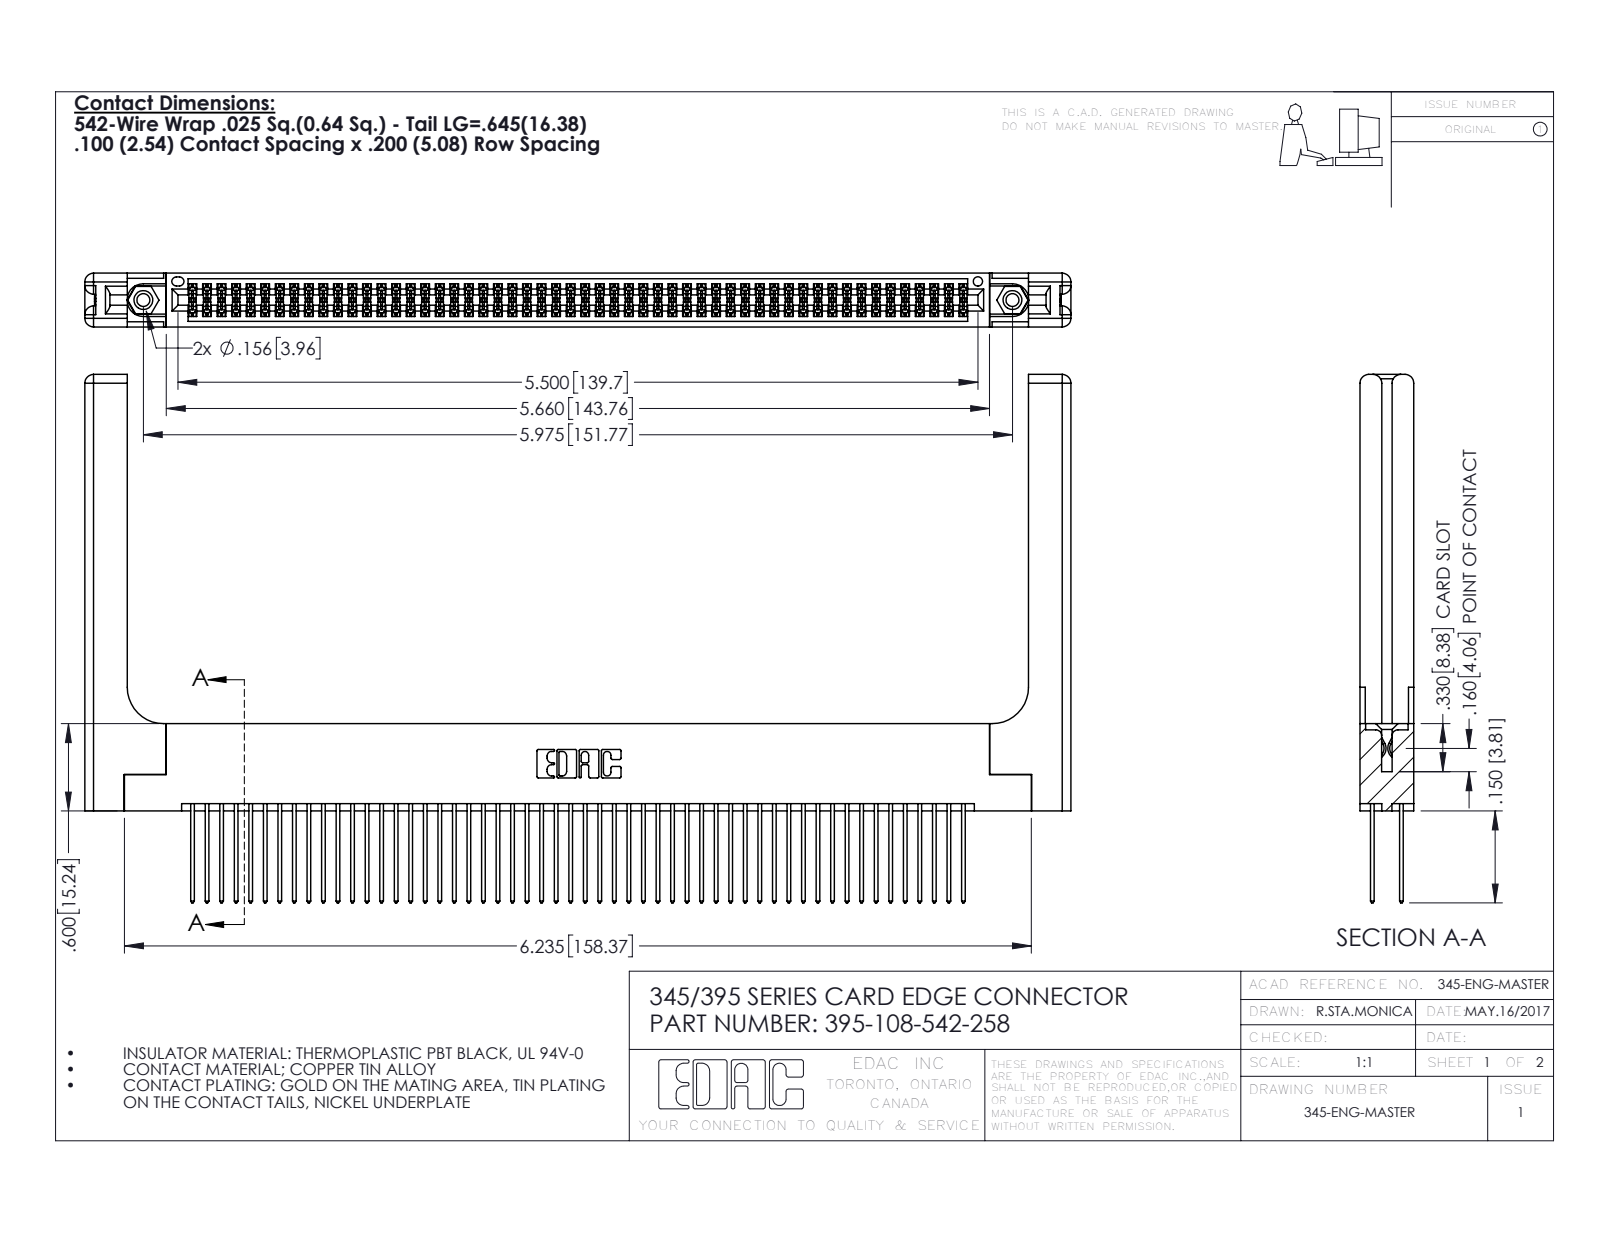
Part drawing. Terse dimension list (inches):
name: 345-250-001_345-250-001-102; 345-220-058_345-220-058; 345 Part_Flush Mounting Lugs - 0.156 Dia-TH; 345-292-001_345-293-142 (+1 more)
written by: SolidWorks 2016 (CONFIG_CONTROL_DESIGN)
unit: in
bodies: 113 solids, 5782 faces (3792 planar, 1930 cylindrical, 60 other)
size: 6.779 × 3.632 × 0.37
volume: 1.575 in³; area: 51.58 in²
holes: 2× ⌀0.089, 2× ⌀0.125, 2× ⌀0.156, 1× ⌀0.064
bosses: 2× ⌀0.155
rounds: 162× R0.006, 108× R0.01, 22× R0.01, 16× R0.06, 6× R0.007, 6× R0.031, 3× R0.026, 2× R0.014
face distances: 0.072, 0.298, 0.2, 0.37, 0.098, 0.272, 0.025, 0.225, 0.175, 0.148
hole spacings: 0.27, 5.739, 5.975
